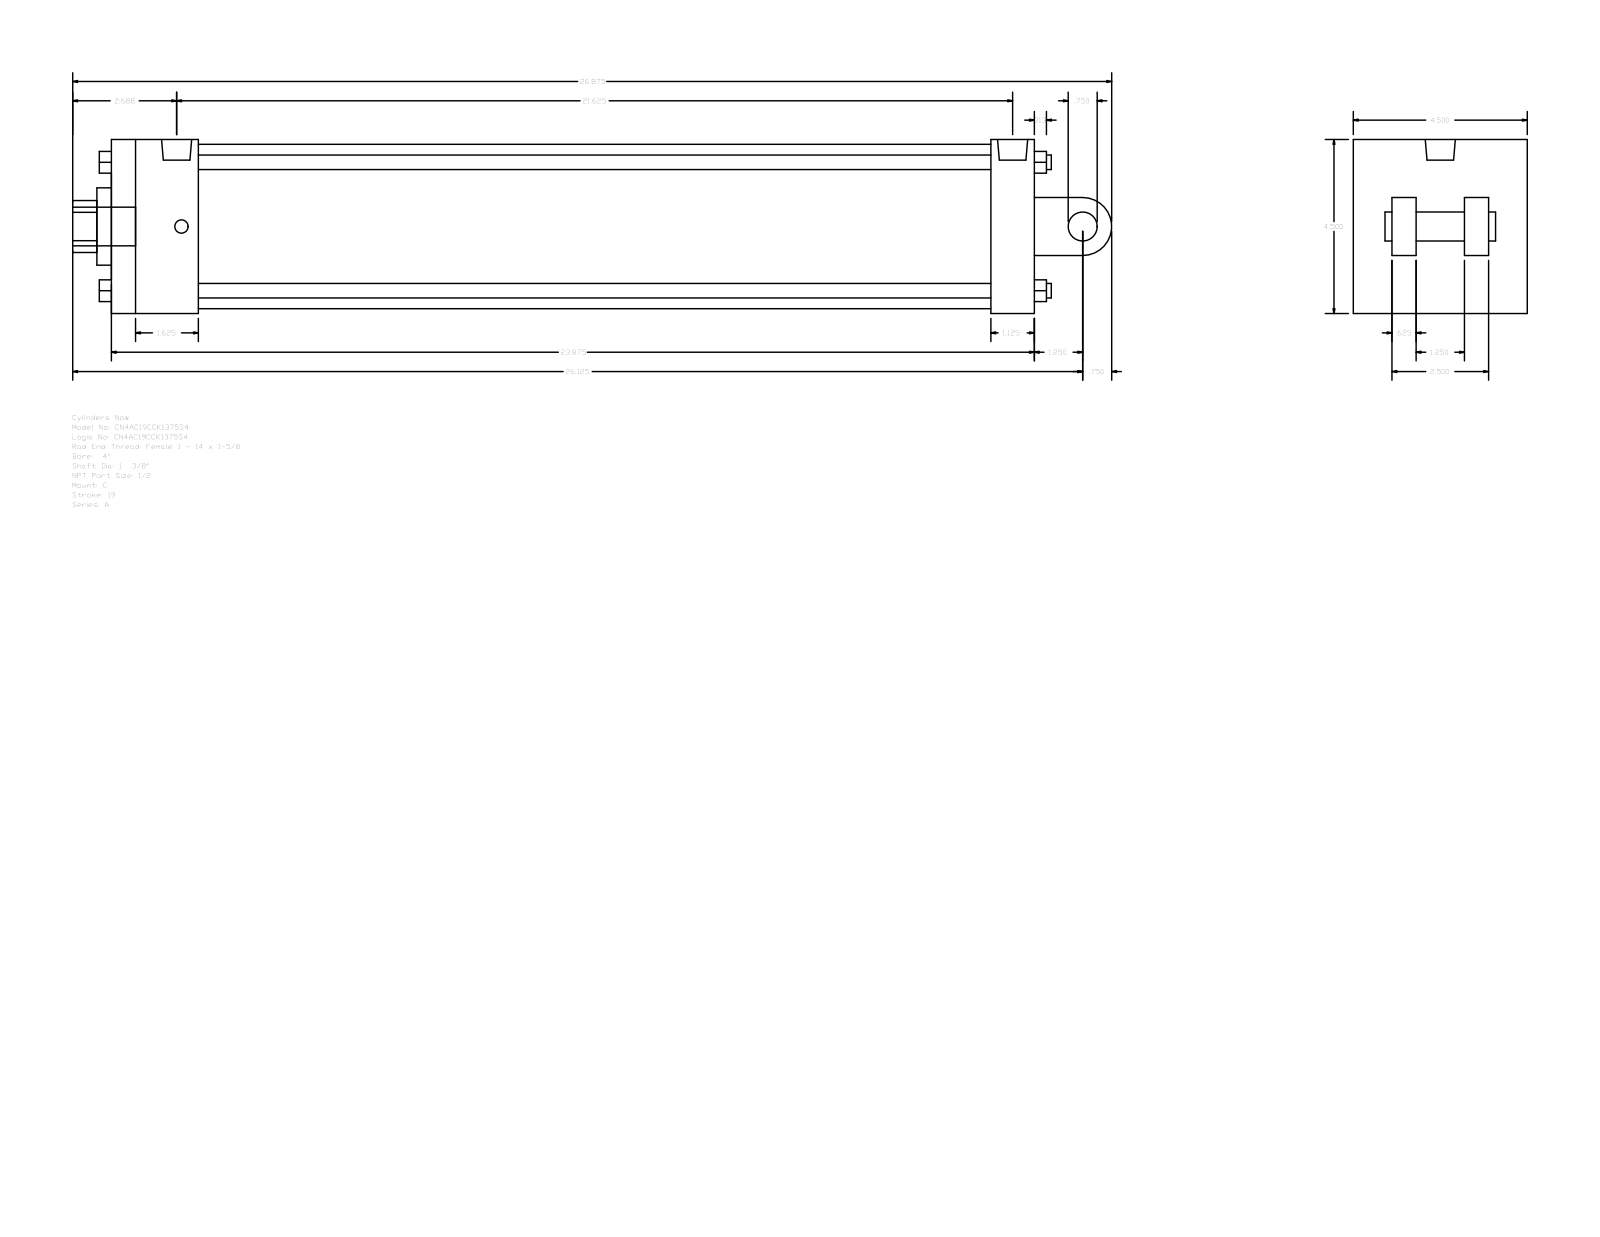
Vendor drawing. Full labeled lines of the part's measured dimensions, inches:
Part name (STEP PRODUCT): A_C__0400_1.375
STEP written by: GSSL Pune (CONFIG_CONTROL_DESIGN)
Units: inches
Bodies: 0 solids, 135 faces (102 planar, 33 cylindrical, 0 other)
Overall size (bounding box): 26.875 × 4.5 × 4.5
Round holes (diameter × count): ⌀0.344 ×2, ⌀0.778 ×1, ⌀1.375 ×1, ⌀2 ×1, ⌀4.25 ×1
Round bosses / shafts (diameter × count): ⌀0.375 ×4, ⌀0.344 ×2, ⌀1 ×1, ⌀0.778 ×1, ⌀0.75 ×1
Partial cylindrical surfaces — rounded edges, fillets, slot ends (radius × count): R0.672 ×1, R0.75 ×1
Main face-to-face distances: 4.5, 23.875, 1.125, 2.875, 22.75, 2.25, 20.5, 21.625, 0.625, 1.625
Hole centre spacings: 0.125
